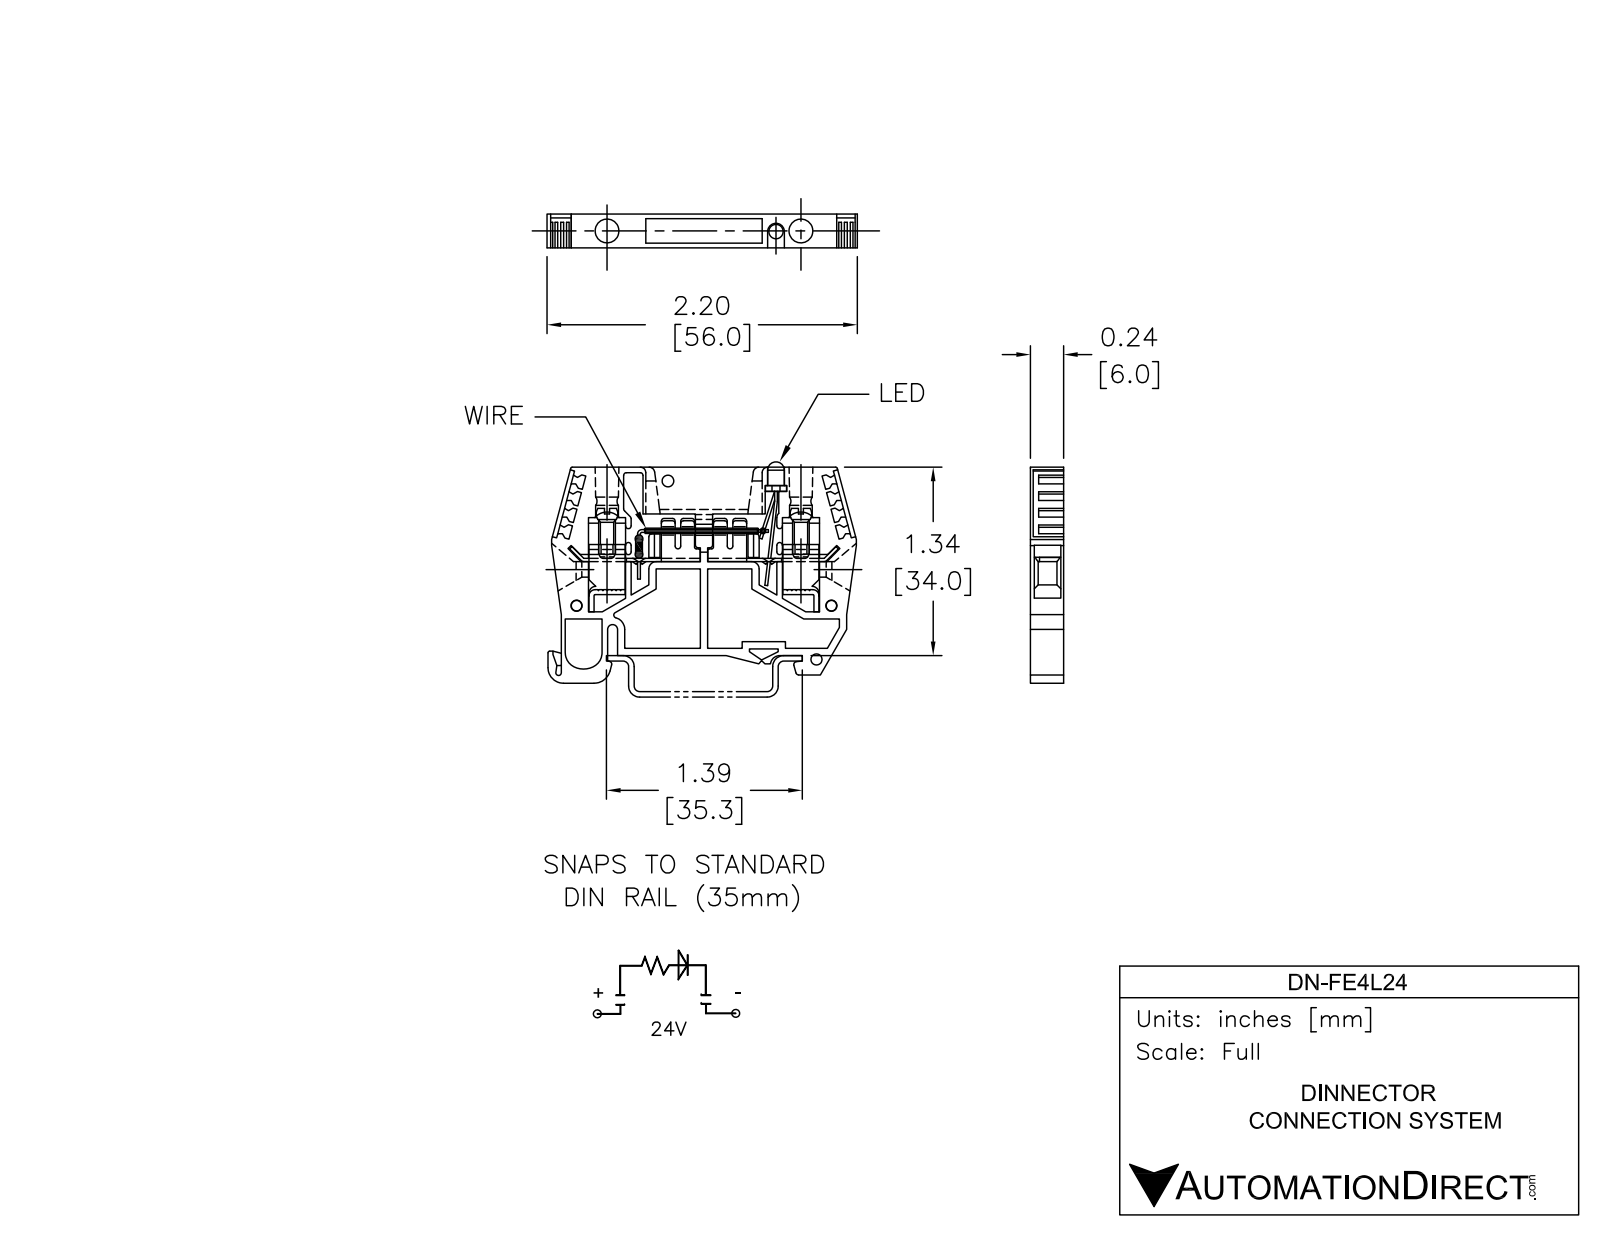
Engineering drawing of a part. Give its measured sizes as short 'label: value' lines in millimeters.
name: 4358100_DN-QFE4; 20621_1; 4358102-DN-FE4L24
written by: SolidWorks 2013 (AUTOMOTIVE_DESIGN)
unit: mm
bodies: 2 solids, 371 faces (227 planar, 91 cylindrical, 53 other)
size: 55.65 × 39.6 × 6
volume: 9 020 mm³; area: 6 676 mm²
holes: 3× ⌀2, 2× ⌀4.1
bosses: 10× ⌀0.3, 1× ⌀4, 1× ⌀3
rounds: 13× R0.5, 5× R3, 3× R1, 2× R1.3, 1× R0.9, 1× R1.05, 1× R1.5, 1× R1.7
face distances: 6, 0.5, 3.5, 2, 2.5, 5.5, 34, 2.2, 1.5, 3
hole spacings: 10.07, 35, 44.38, 46
